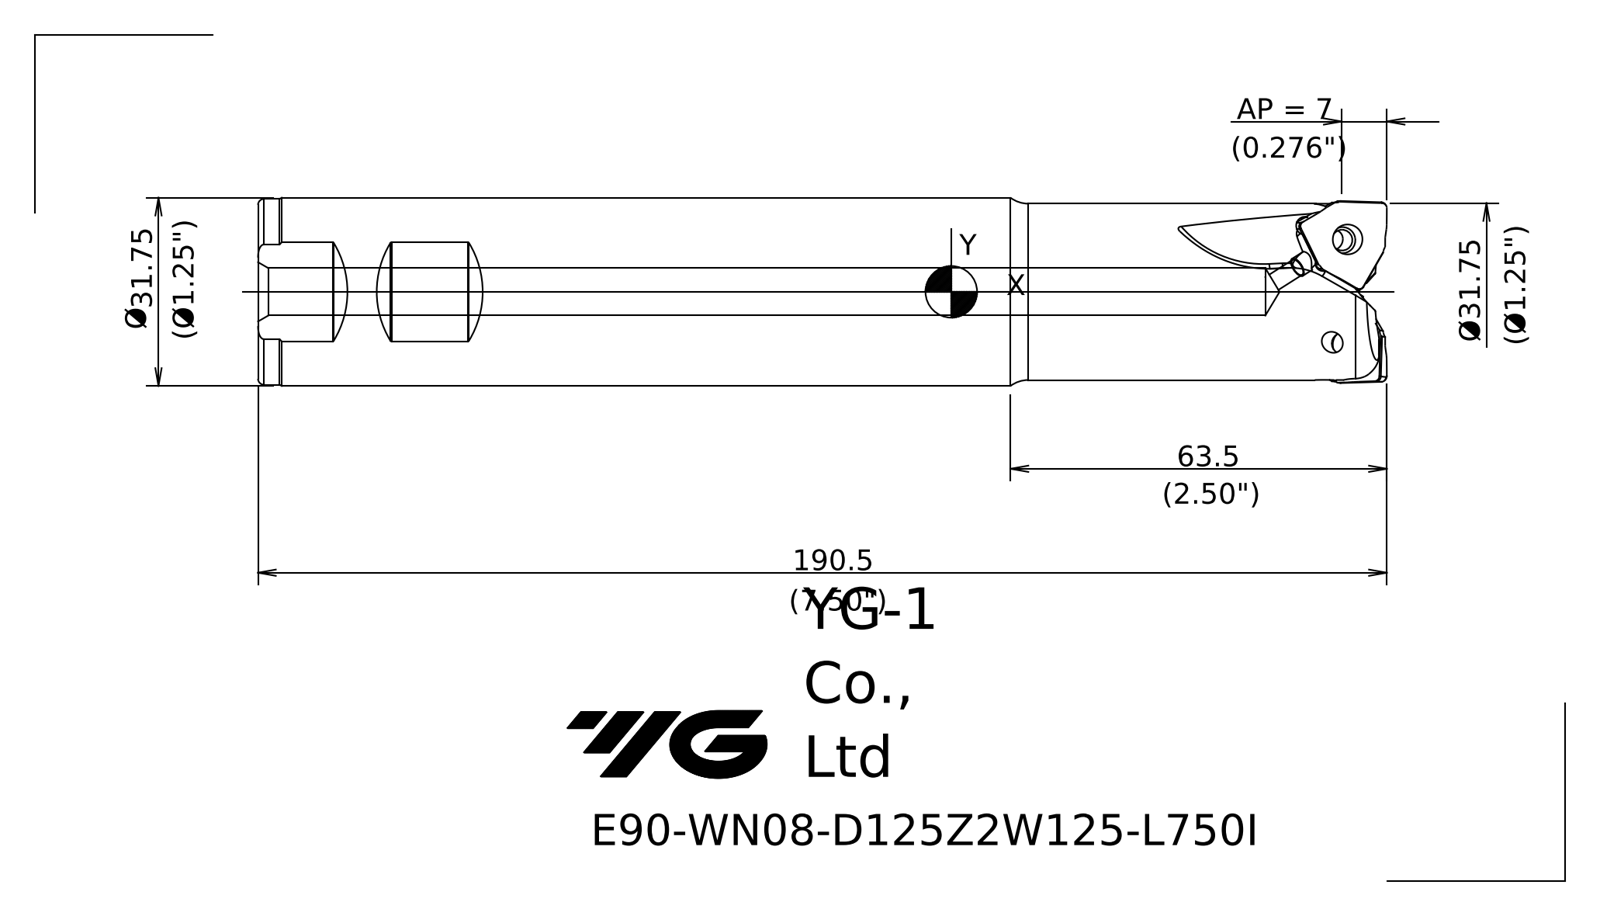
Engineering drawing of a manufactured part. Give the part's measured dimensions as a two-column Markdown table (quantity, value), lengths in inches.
| quantity | value |
| --- | --- |
| part name | 10224990B0573za9 |
| STEP written by | SIEMENS PLM Software NX 10.0 (AP203_CONFIGURATION_CONTROLLED_3D_DESIGN_OF_MECHANICAL_PARTS_AND_ASSEMBLIES_MIM_LF) |
| units | inches |
| bodies | 1 solid, 63 faces (8 planar, 7 cylindrical, 48 other) |
| overall size | 7.5 × 1.25 × 1.25 |
| volume | 8.163 in³ |
| surface area | 41.91 in² |
| round holes (diameter × count) | 0.315 × 1 |
| round bosses / shafts (diameter × count) | 1.25 × 1, 1.234 × 1, 1.171 × 1 |
| partial cylindrical surfaces (radius × count) | 0.012 × 3 |
| main face-to-face distances | 7.449, 0.635, 0.126, 7.323 |
